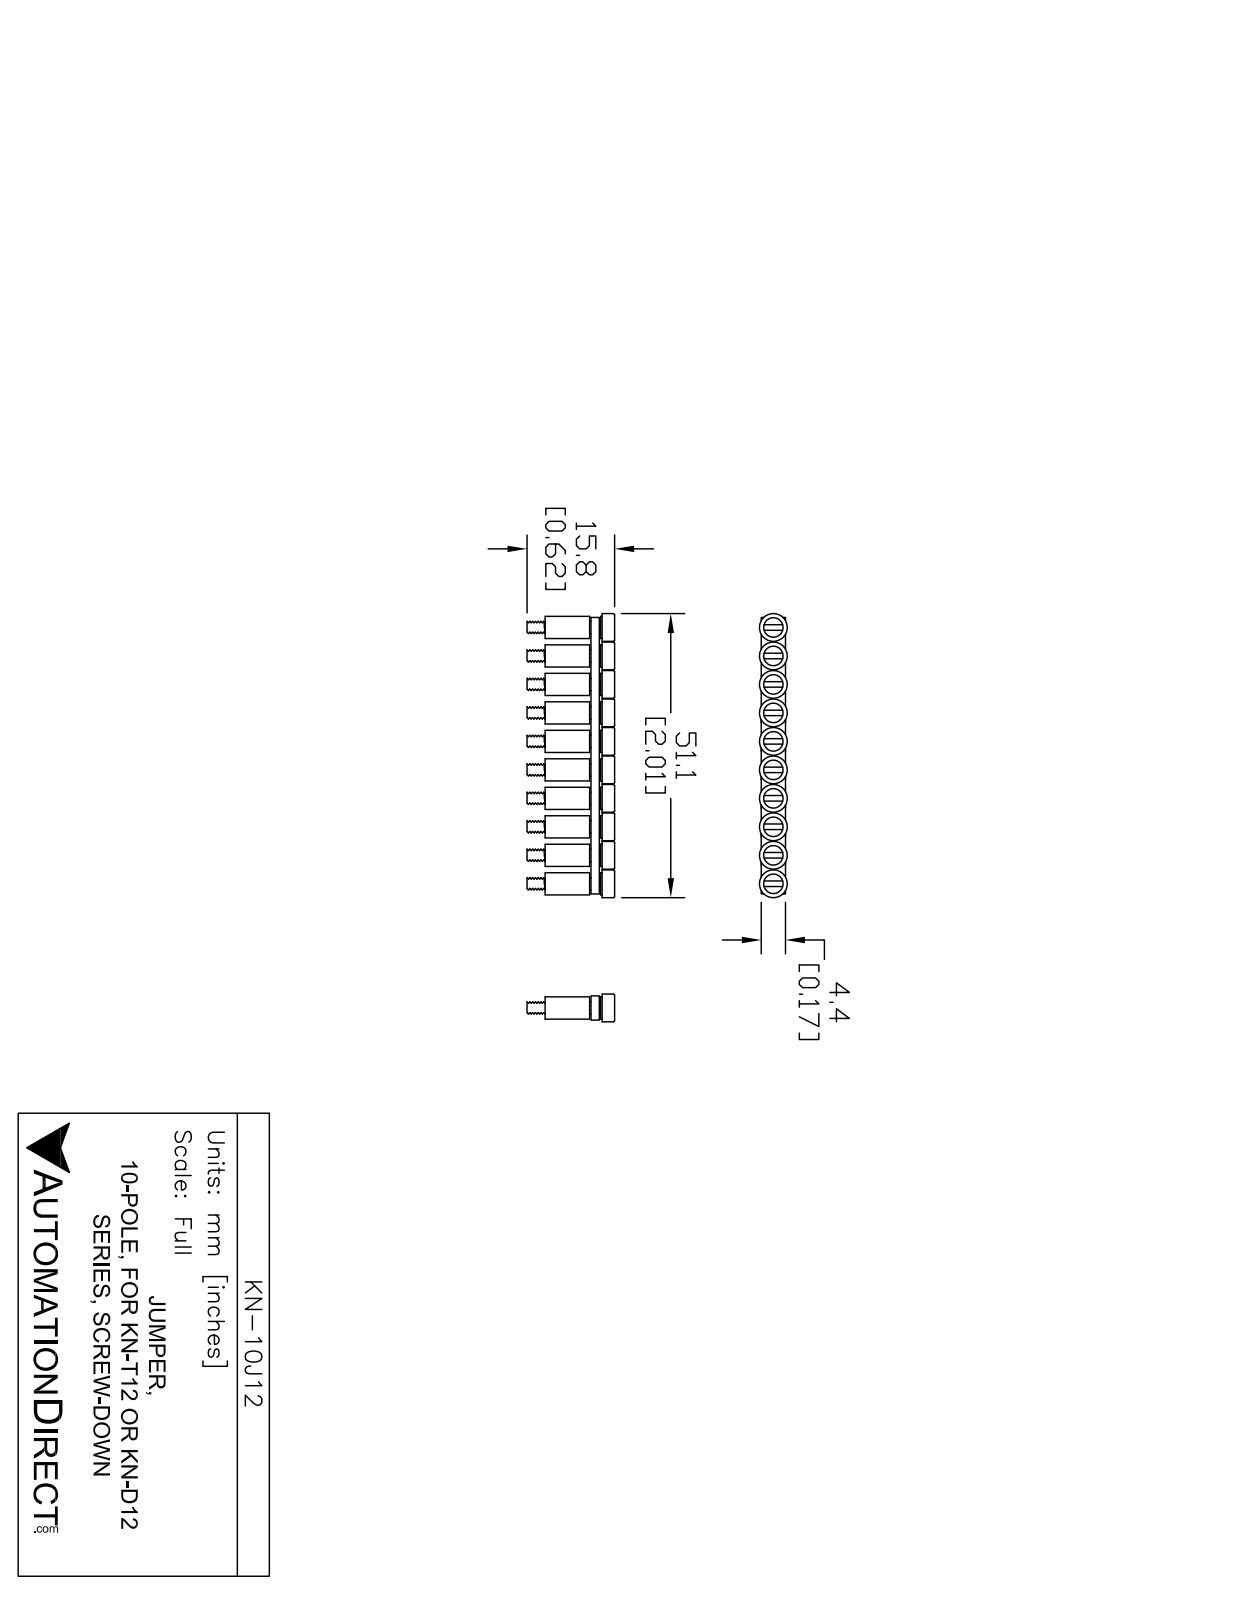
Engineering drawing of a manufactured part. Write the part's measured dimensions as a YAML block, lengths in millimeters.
part_name: "KN-10J12"
step_written_by: "SolidWorks 2014 (AUTOMOTIVE_DESIGN)"
units: millimeters
bodies: {solids: 31, faces: 326, planar: 136, cylindrical: 130, other: 60}
overall_size: [50, 15.75, 5]
volume: 1680
surface_area: 4814
round_holes:
  - {diameter: 3, count: 10}
  - {diameter: 3.5, count: 10}
round_bosses_or_shafts:
  - {diameter: 5, count: 10}
  - {diameter: 4, count: 10}
  - {diameter: 2.25, count: 10}
face_to_face_distances: [1.5, 2, 1.75, 2.25, 0.5, 1, 10, 2.75, 3.75, 4]
hole_center_spacings: [5, 10, 15, 20, 25, 30, 35, 40]
